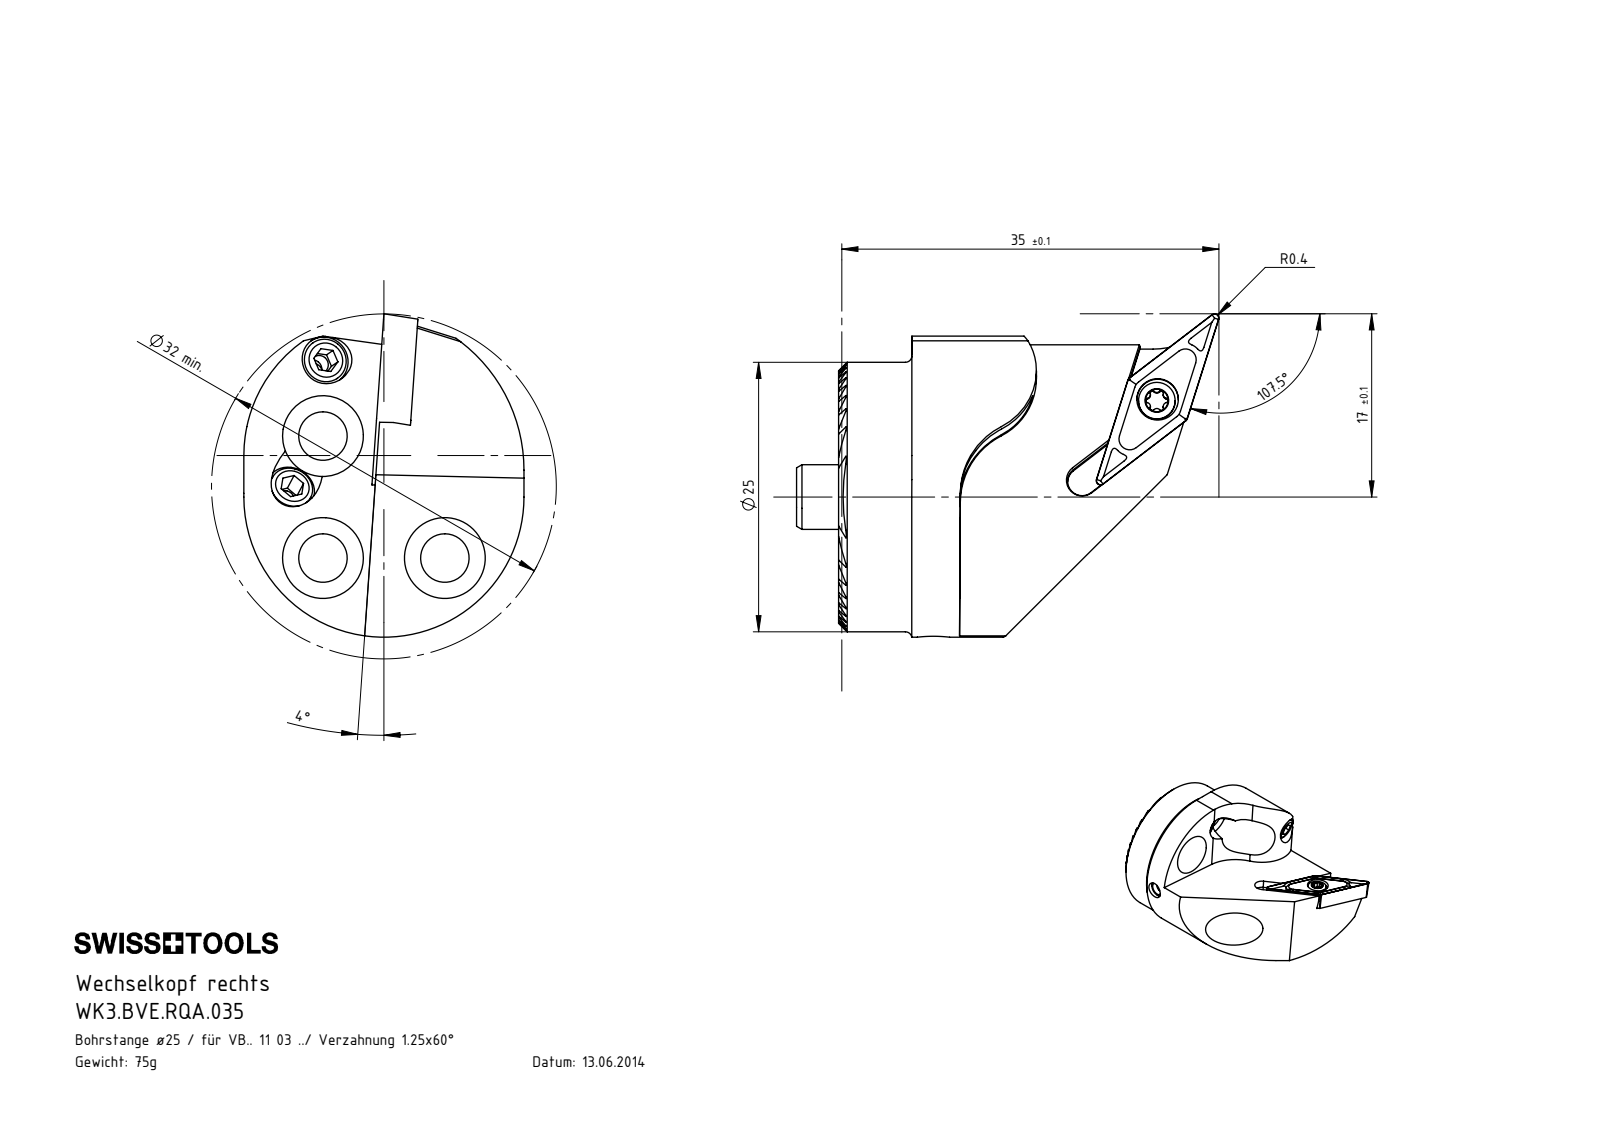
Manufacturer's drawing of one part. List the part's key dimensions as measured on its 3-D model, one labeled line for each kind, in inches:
Part name (STEP PRODUCT): KVT_MB_600_030; WCA-ER2.001.006_A; WK3-ER1.001.006_A_Fertigbearbeitung; WK3-BVE.RQA.035_A_Fertigbearbeitung (+3 more)
STEP written by: SolidWorks 2017 (AUTOMOTIVE_DESIGN)
Units: inches
Bodies: 12 solids, 523 faces (180 planar, 174 cylindrical, 169 other)
Overall size (bounding box): 1.543 × 1.181 × 1.024
Volume: 0.571 in³ · Surface area: 9.639 in²
Round holes (diameter × count): ⌀0.177 ×5, ⌀0.094 ×3, ⌀0.098 ×3, ⌀0.295 ×3, ⌀0.067 ×2, ⌀0.118 ×2, ⌀0.13 ×2, ⌀0.081 ×1, ⌀0.11 ×1, ⌀0.152 ×1, ⌀0.165 ×1, ⌀0.236 ×1
Round bosses / shafts (diameter × count): ⌀0.118 ×3, ⌀0.157 ×2, ⌀0.984 ×1, ⌀0.134 ×1, ⌀0.098 ×1
Partial cylindrical surfaces — rounded edges, fillets, slot ends (radius × count): R0.005 ×20, R0.008 ×6, R0.014 ×5, R0.276 ×2, R0.512 ×2, R0.014 ×1, R0.053 ×1, R0.236 ×1
Main face-to-face distances: 0.17, 0.043, 0.128, 0.213, 0.341, 0.298, 0.085, 0.085, 0.383, 0.256
Hole centre spacings: 0.315, 0.446, 0.63
